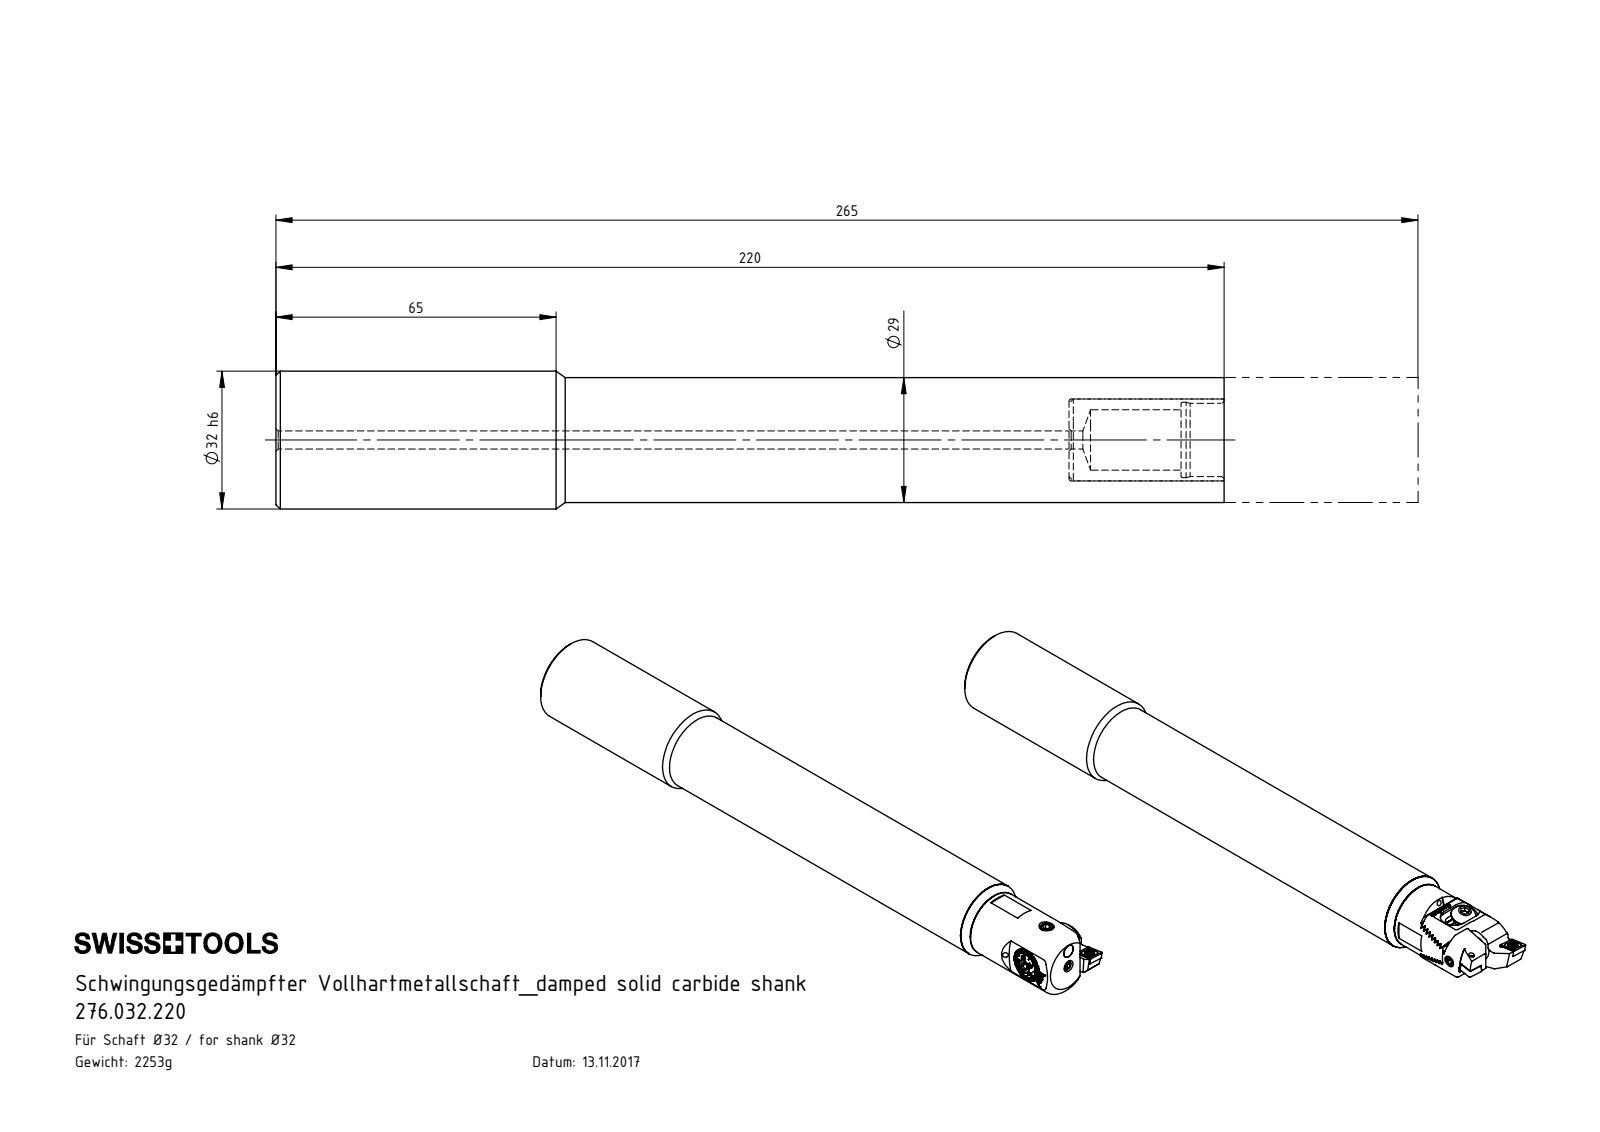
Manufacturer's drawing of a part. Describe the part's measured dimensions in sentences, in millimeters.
The part is named "HP5-ER1.019.036_A; U32-HP5.029.220_A; U32.HP5.029.220". Its 3-D file was written by "SolidWorks 2017 (AUTOMOTIVE_DESIGN)". It is 2 solids with 25 faces: 6 planar, 9 cylindrical and 10 other. Overall it measures 220 by 32 by 32 millimeters. Its volume is 146 478 cubic millimeters and its surface area 30 796 square millimeters. Round holes: 1 of diameter 4.2, 1 of diameter 14, 1 of diameter 17, 1 of diameter 17.5, 1 of diameter 19. Round bosses or shafts: 1 of diameter 32, 1 of diameter 29. The main face-to-face distances are 184, 220, 36, 210, 26, 10.
